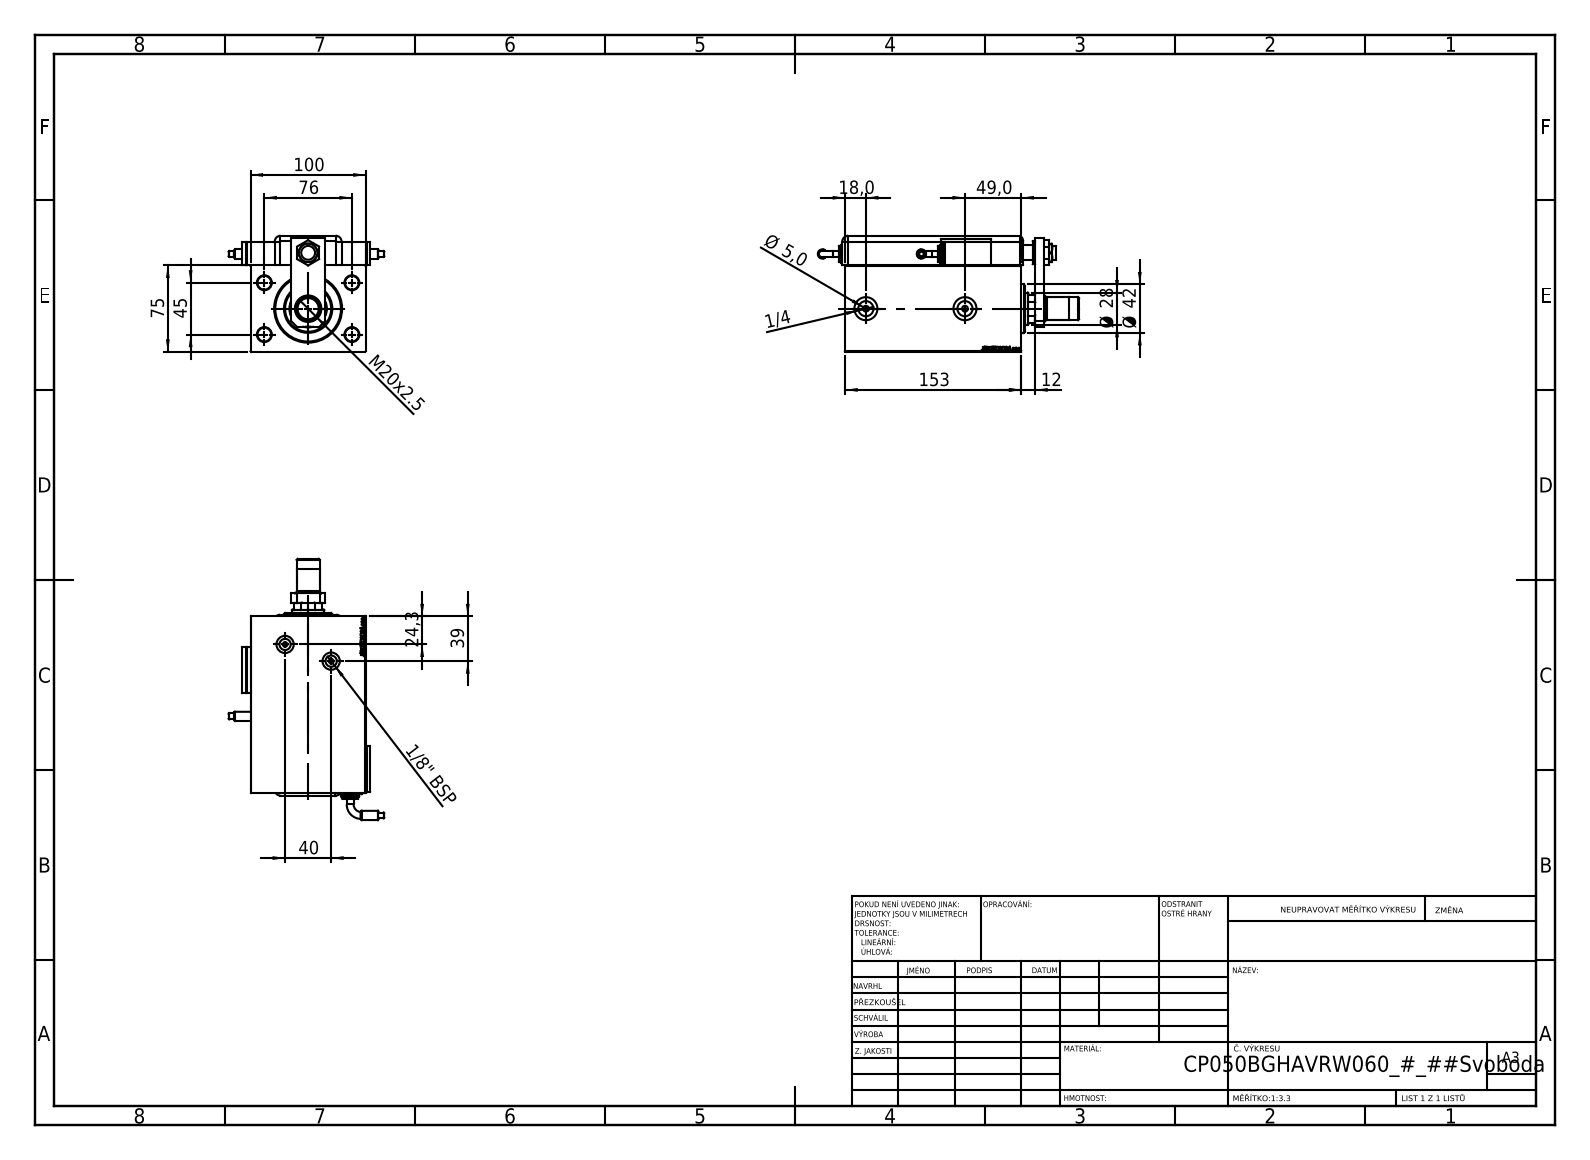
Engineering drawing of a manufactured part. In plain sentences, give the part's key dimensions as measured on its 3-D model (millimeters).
The part is named "SWITCH_Q_FRONT_BACK; V450CP_B; NUT_D19; ZARAZKA_Q (+7 more)". Its 3-D file was written by "SolidWorks 2019 (CONFIG_CONTROL_DESIGN)". It is 15 solids with 1344 faces: 624 planar, 139 cylindrical and 581 other. Overall it measures 226.76 by 135.01 by 100.8 millimeters. Its volume is 1 231 000 cubic millimeters and its surface area 210 643 square millimeters. Round holes: 5 of diameter 12, 4 of diameter 4, 2 of diameter 5, 2 of diameter 8, 2 of diameter 9.73, 2 of diameter 13.16, 2 of diameter 15, 2 of diameter 20, 1 of diameter 13, 1 of diameter 14, 1 of diameter 18.5, 1 of diameter 28. Round bosses or shafts: 4 of diameter 20, 2 of diameter 16, 2 of diameter 14, 2 of diameter 8, 2 of diameter 6, 2 of diameter 5.04, 1 of diameter 42, 1 of diameter 18. Partial cylindrical surfaces (rounded edges, fillets, slot ends): 9 of radius 5, 1 of radius 10, 1 of radius 13.5. The main face-to-face distances are 75, 3, 100, 25.8, 100.8, 20, 14, 97.8, 153, 22.8. The hole center spacings are 44.16, 45, 46.04, 76, 80.53, 88.32, 18.28, 20.
